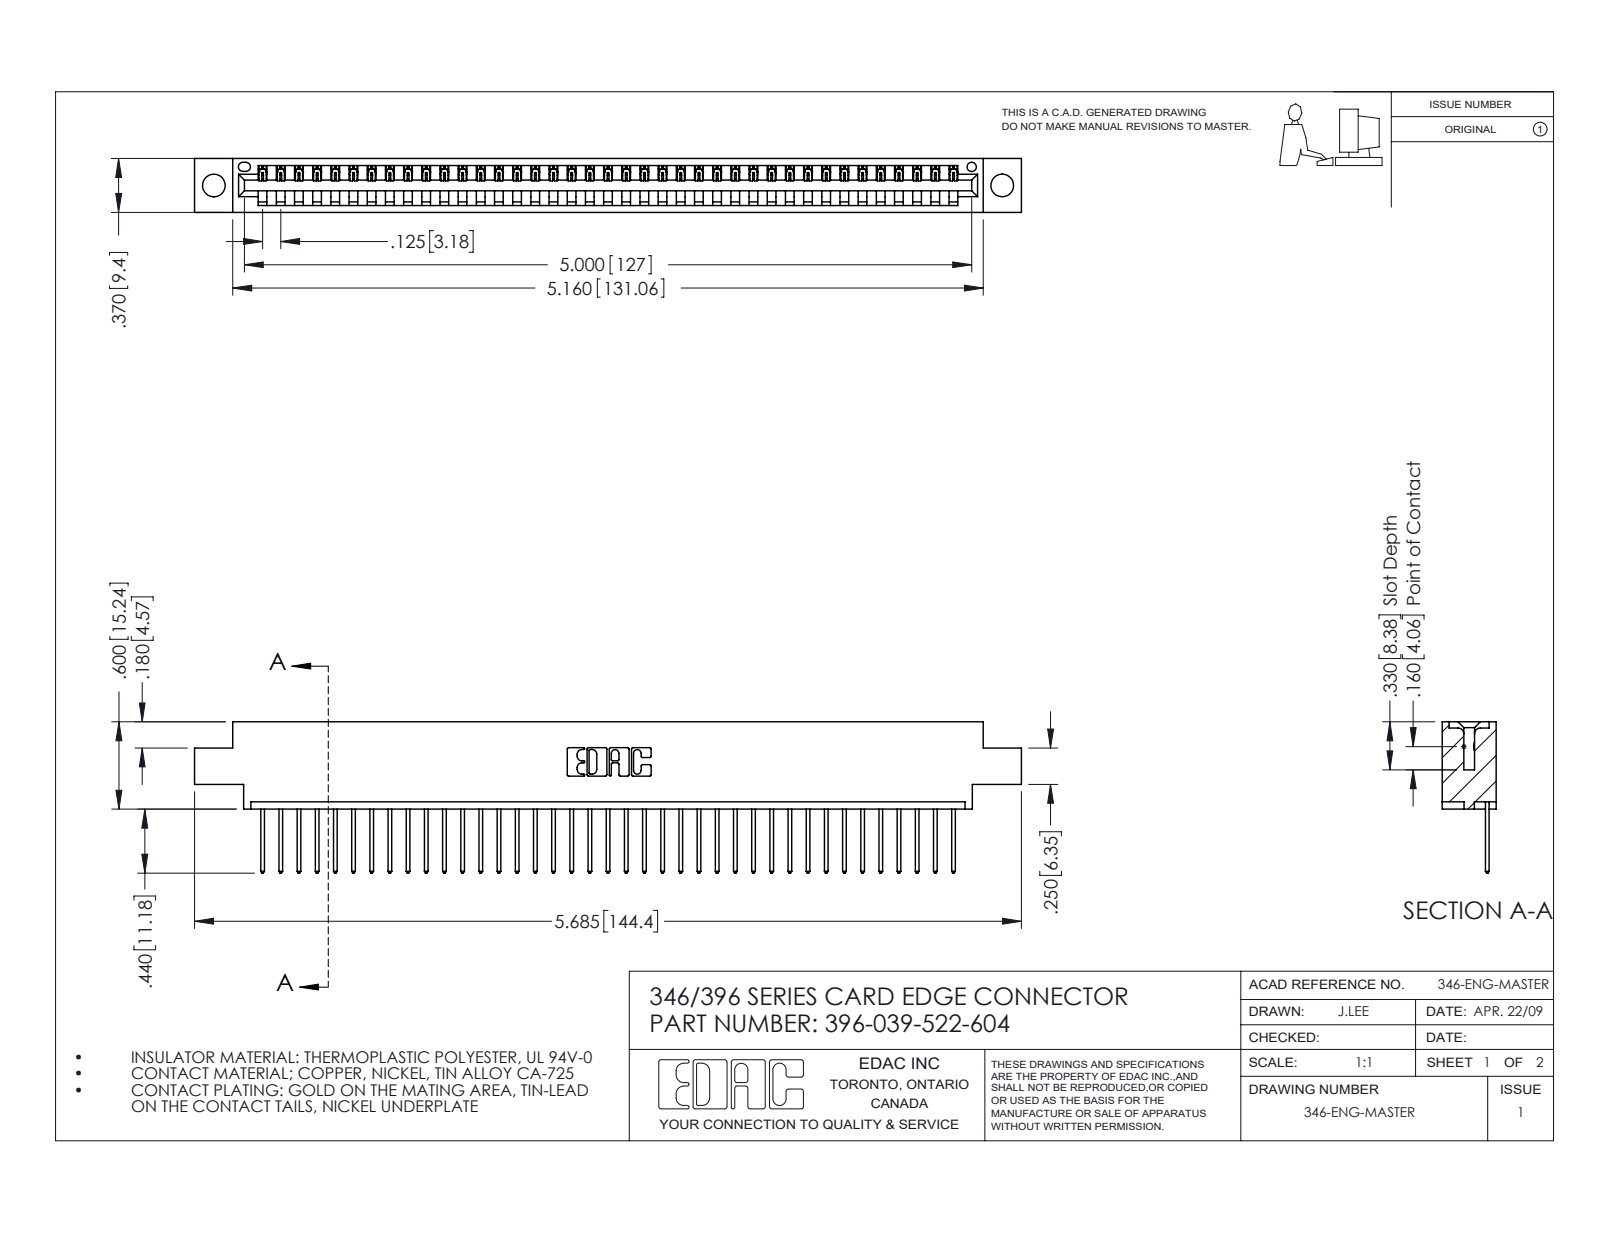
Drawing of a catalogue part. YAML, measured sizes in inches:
part_name: "346 Part_0.170 Offset - 0.156 Dia-TH; 345-292-001_345-293-122; 396-039-522-604"
step_written_by: "SolidWorks 2016 (CONFIG_CONTROL_DESIGN)"
units: inches
bodies: {solids: 40, faces: 2388, planar: 1640, cylindrical: 748, other: 0}
overall_size: [5.685, 1.04, 0.37]
volume: 0.828
surface_area: 26.4
round_holes:
  - {diameter: 0.156, count: 2}
  - {diameter: 0.064, count: 1}
partial_cylinders:
  - {radius: 0.006, count: 78}
  - {radius: 0.01, count: 78}
  - {radius: 0.01, count: 22}
  - {radius: 0.007, count: 6}
  - {radius: 0.031, count: 6}
  - {radius: 0.026, count: 3}
  - {radius: 0.031, count: 2}
  - {radius: 0.04, count: 2}
face_to_face_distances: [0.048, 0.322, 0.37, 0.25, 0.072, 0.298, 0.025, 0.148, 0.222, 0.1]
hole_center_spacings: [0.246, 5.211, 5.42]
